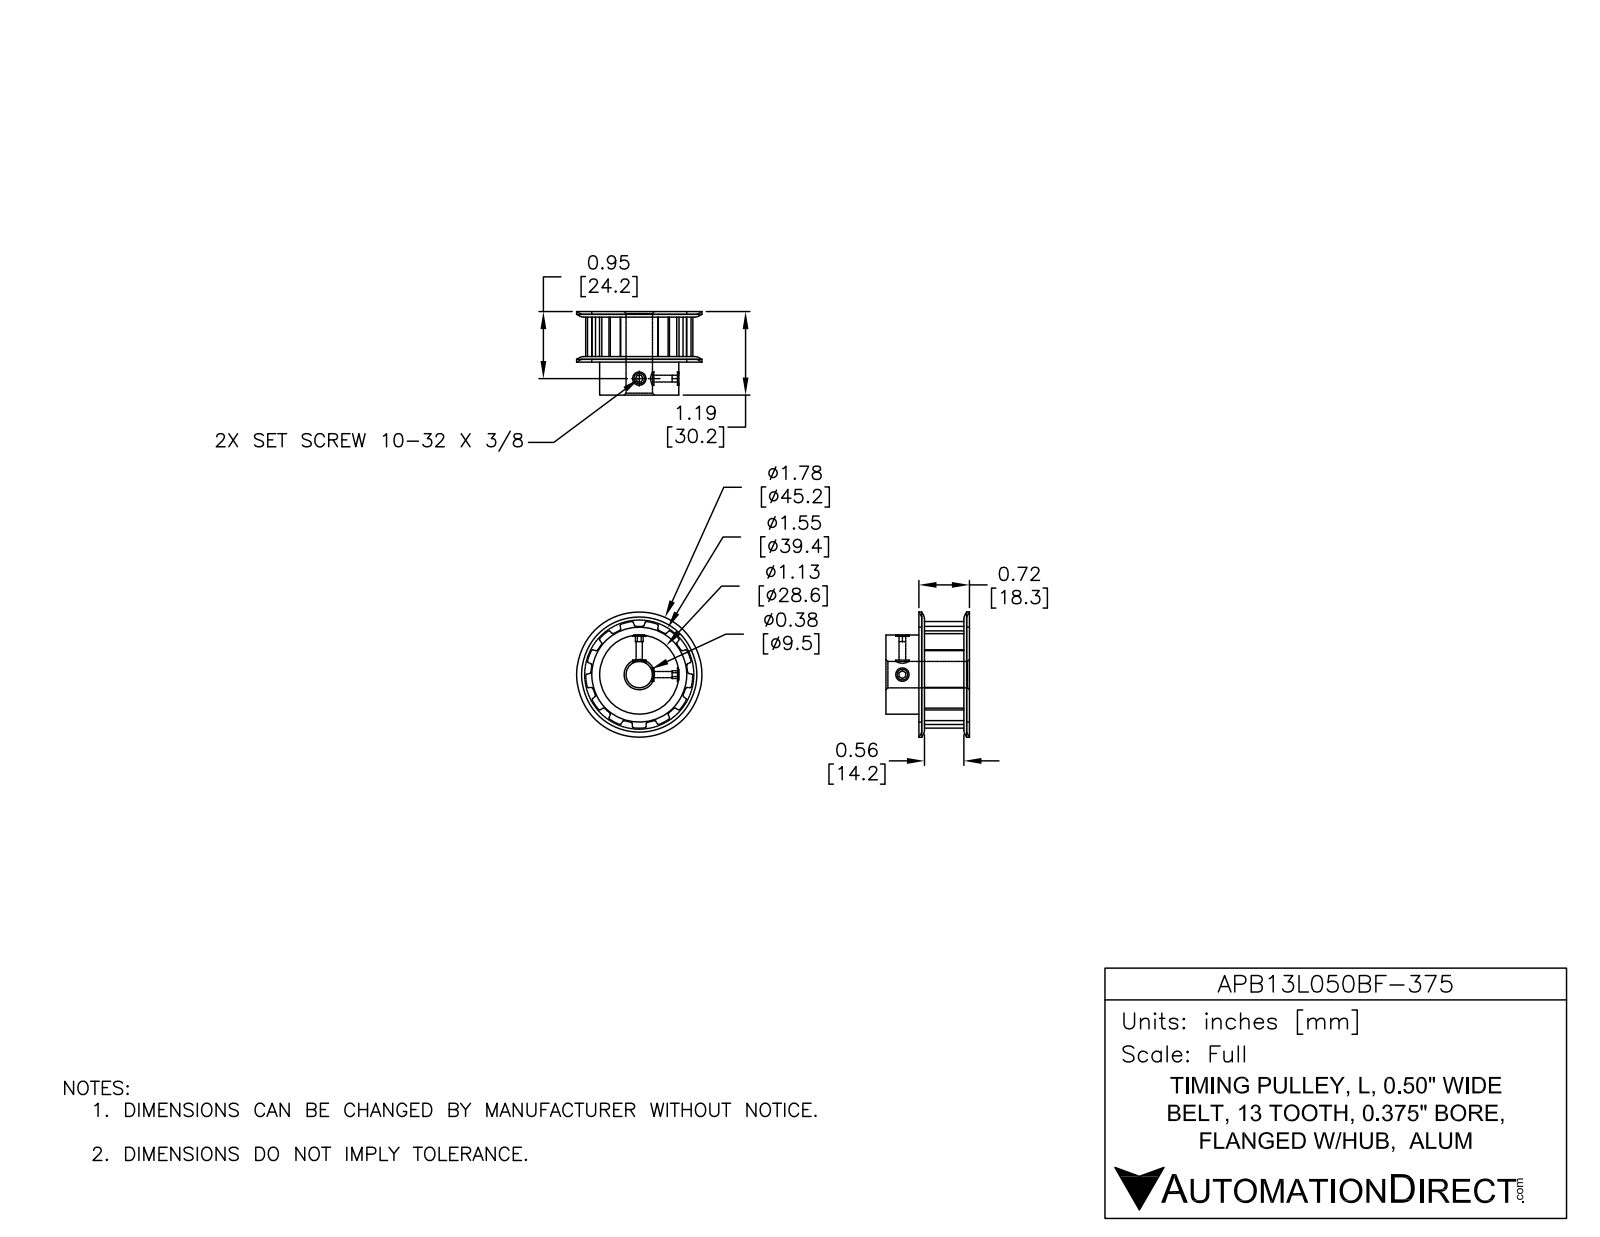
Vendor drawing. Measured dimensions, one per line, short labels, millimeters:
name: APB13L050BF-375
written by: SolidWorks 2014 (AUTOMOTIVE_DESIGN)
unit: mm
bodies: 1 solid, 122 faces (45 planar, 55 cylindrical, 22 other)
size: 45.2 × 45.2 × 30.2
volume: 26 280 mm³; area: 8 587 mm²
holes: 2× ⌀2.2, 1× ⌀9.5
bosses: 1× ⌀28.6
rounds: 26× R0.4, 1× R17.9
face distances: 16.3, 1, 17.3, 30.2, 29.2, 12.9, 1, 15.2, 2, 28.1
